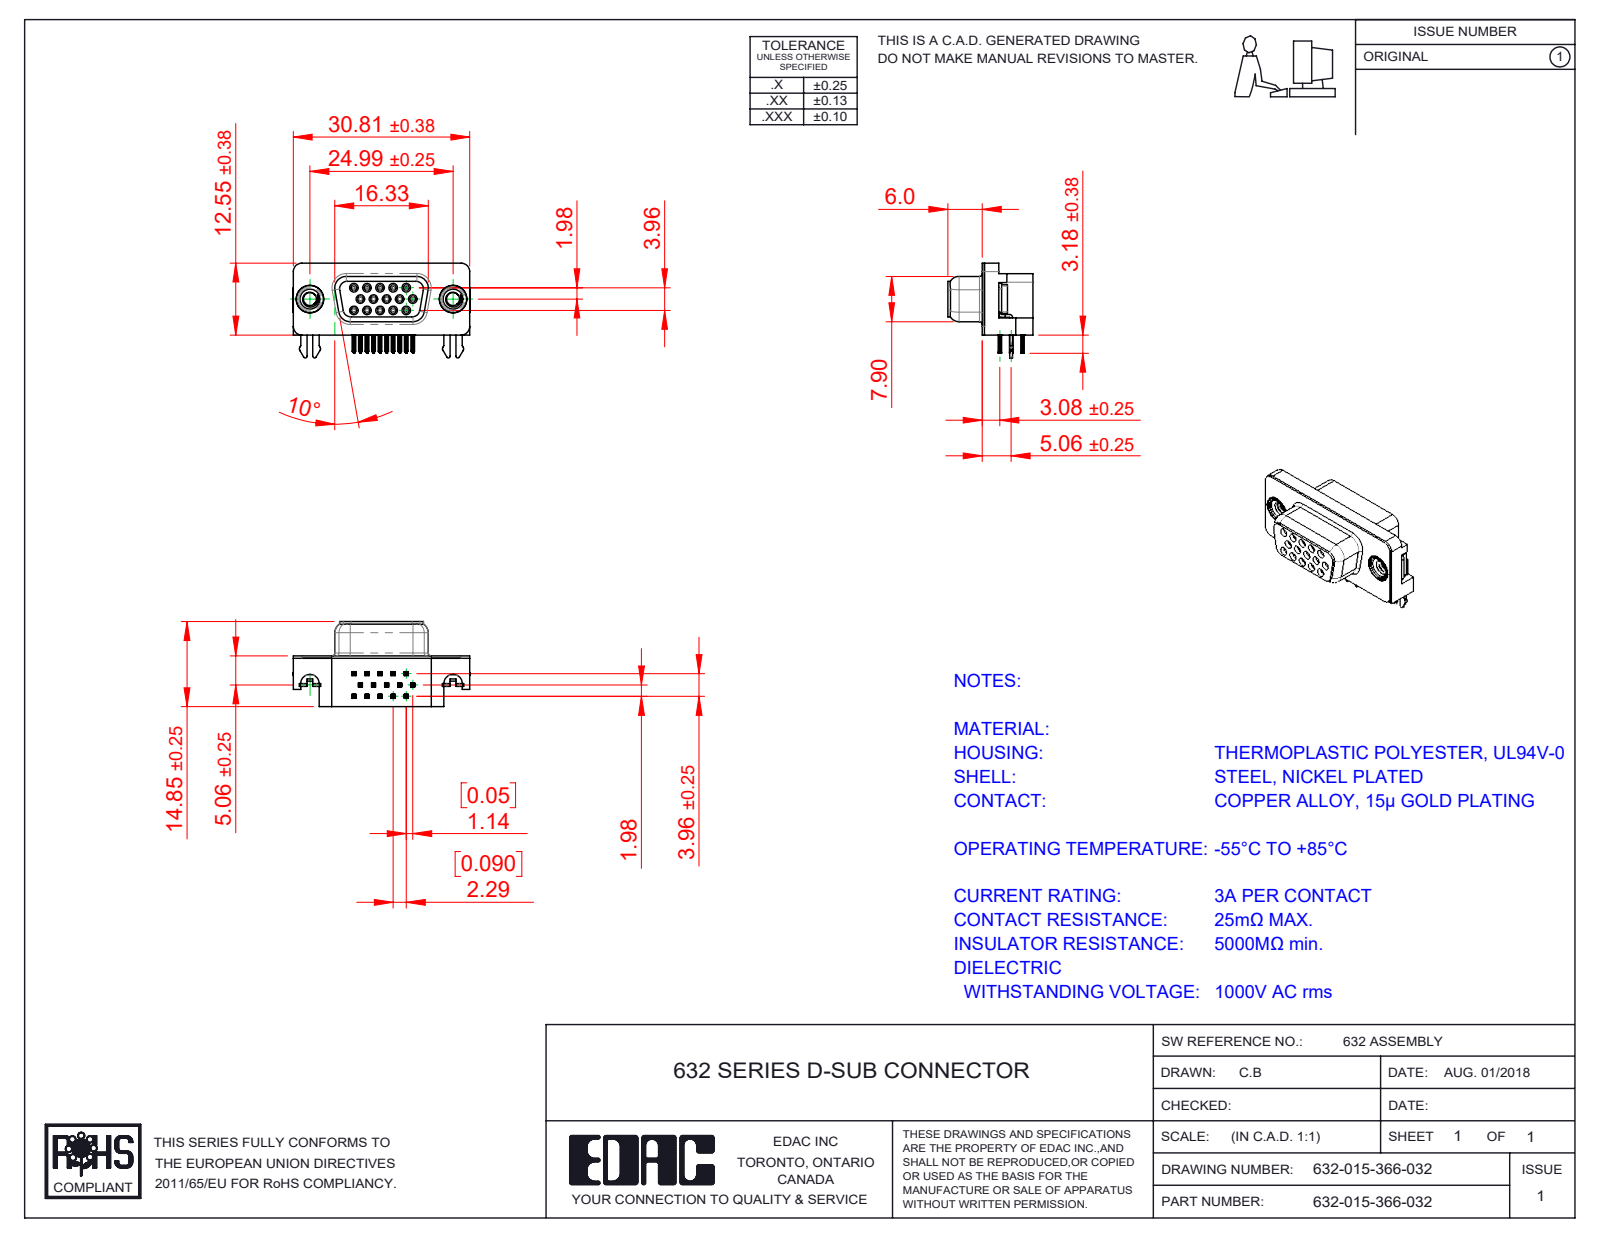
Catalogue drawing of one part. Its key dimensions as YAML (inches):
part_name: "632 4-40 Threaded Rivet; 632 2 Prong Board Lock; 632 Contact Top; 632 Contact Bottom (+4 more)"
step_written_by: "SolidWorks 2016 (CONFIG_CONTROL_DESIGN)"
units: inches
bodies: {solids: 21, faces: 2338, planar: 990, cylindrical: 612, other: 736}
overall_size: [1.216, 0.652, 0.585]
volume: 0.178
surface_area: 7.778
round_holes:
  - {diameter: 0.031, count: 15}
  - {diameter: 0.035, count: 15}
  - {diameter: 0.089, count: 2}
  - {diameter: 0.157, count: 2}
  - {diameter: 0.189, count: 2}
  - {diameter: 0.197, count: 2}
round_bosses_or_shafts:
  - {diameter: 0.047, count: 15}
  - {diameter: 0.193, count: 2}
  - {diameter: 0.187, count: 2}
  - {diameter: 0.154, count: 2}
partial_cylinders:
  - {radius: 0.004, count: 120}
  - {radius: 0.006, count: 60}
  - {radius: 0.014, count: 30}
  - {radius: 0.013, count: 15}
  - {radius: 0.039, count: 11}
  - {radius: 0.011, count: 10}
  - {radius: 0.02, count: 10}
  - {radius: 0.01, count: 8}
face_to_face_distances: [0.016, 0.078, 0.333, 0.348, 0.114, 0.098, 0.234, 0.252, 0.264, 0.278]
hole_center_spacings: [0.09, 0.09, 0.156, 0.18, 0.238, 0.156, 0.18, 0.27]
